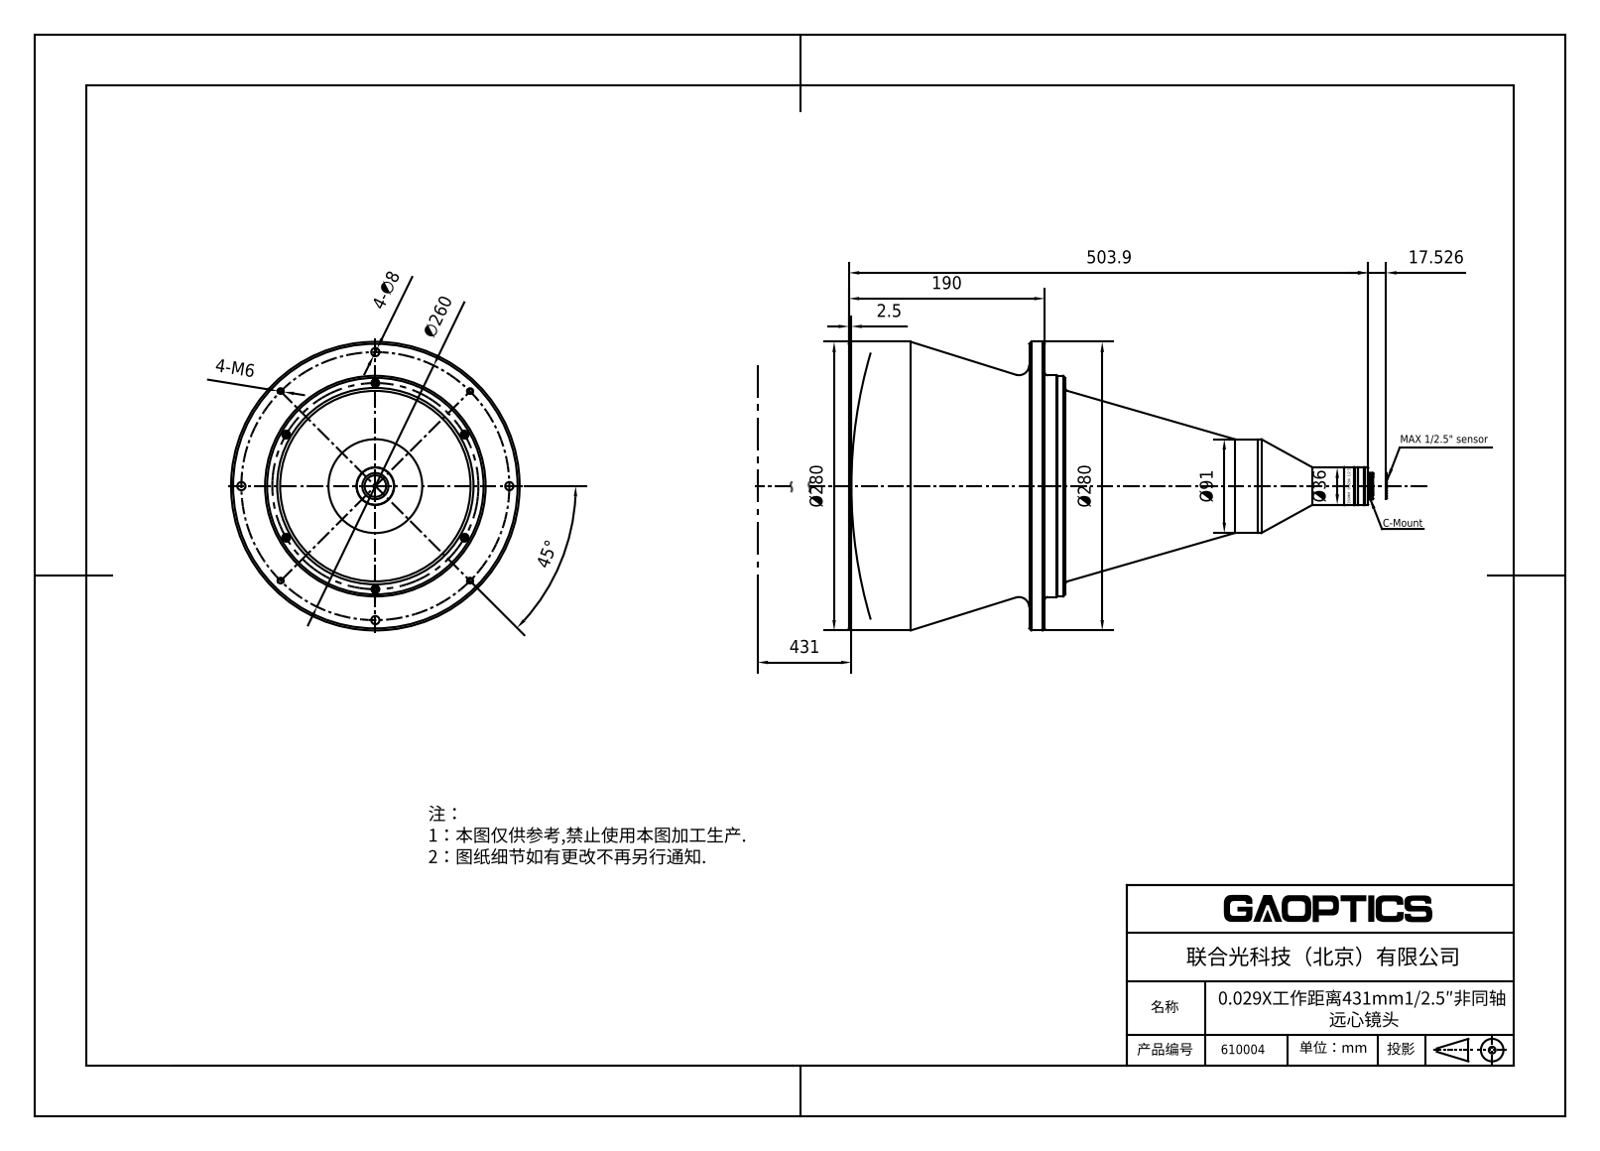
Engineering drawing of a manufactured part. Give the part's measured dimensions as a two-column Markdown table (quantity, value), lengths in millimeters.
| quantity | value |
| --- | --- |
| part name | 610004 |
| STEP written by | SolidWorks 2020 (CONFIG_CONTROL_DESIGN) |
| units | millimeters |
| bodies | 0 solids, 822 faces (305 planar, 116 cylindrical, 401 other) |
| overall size | 509.25 × 280 × 280 |
| round holes (diameter × count) | 7 × 6, 25.4 × 1, 31.6 × 1, 35.4 × 1, 36 × 1, 36.6 × 1, 91 × 1, 214 × 1, 215 × 1, 280 × 1 |
| round bosses / shafts (diameter × count) | 7.5 × 6, 8 × 4, 5 × 4, 265.8 × 1, 256.2 × 1, 20.4 × 1 |
| partial cylindrical surfaces (radius × count) | 18.1 × 1, 18.2 × 1, 18.25 × 1 |
| main face-to-face distances | 157.35, 15, 142.35, 345.24, 202.89, 187.89, 177.35, 35, 20, 167.89 |
| hole center spacings | 100, 173.2, 200 |
